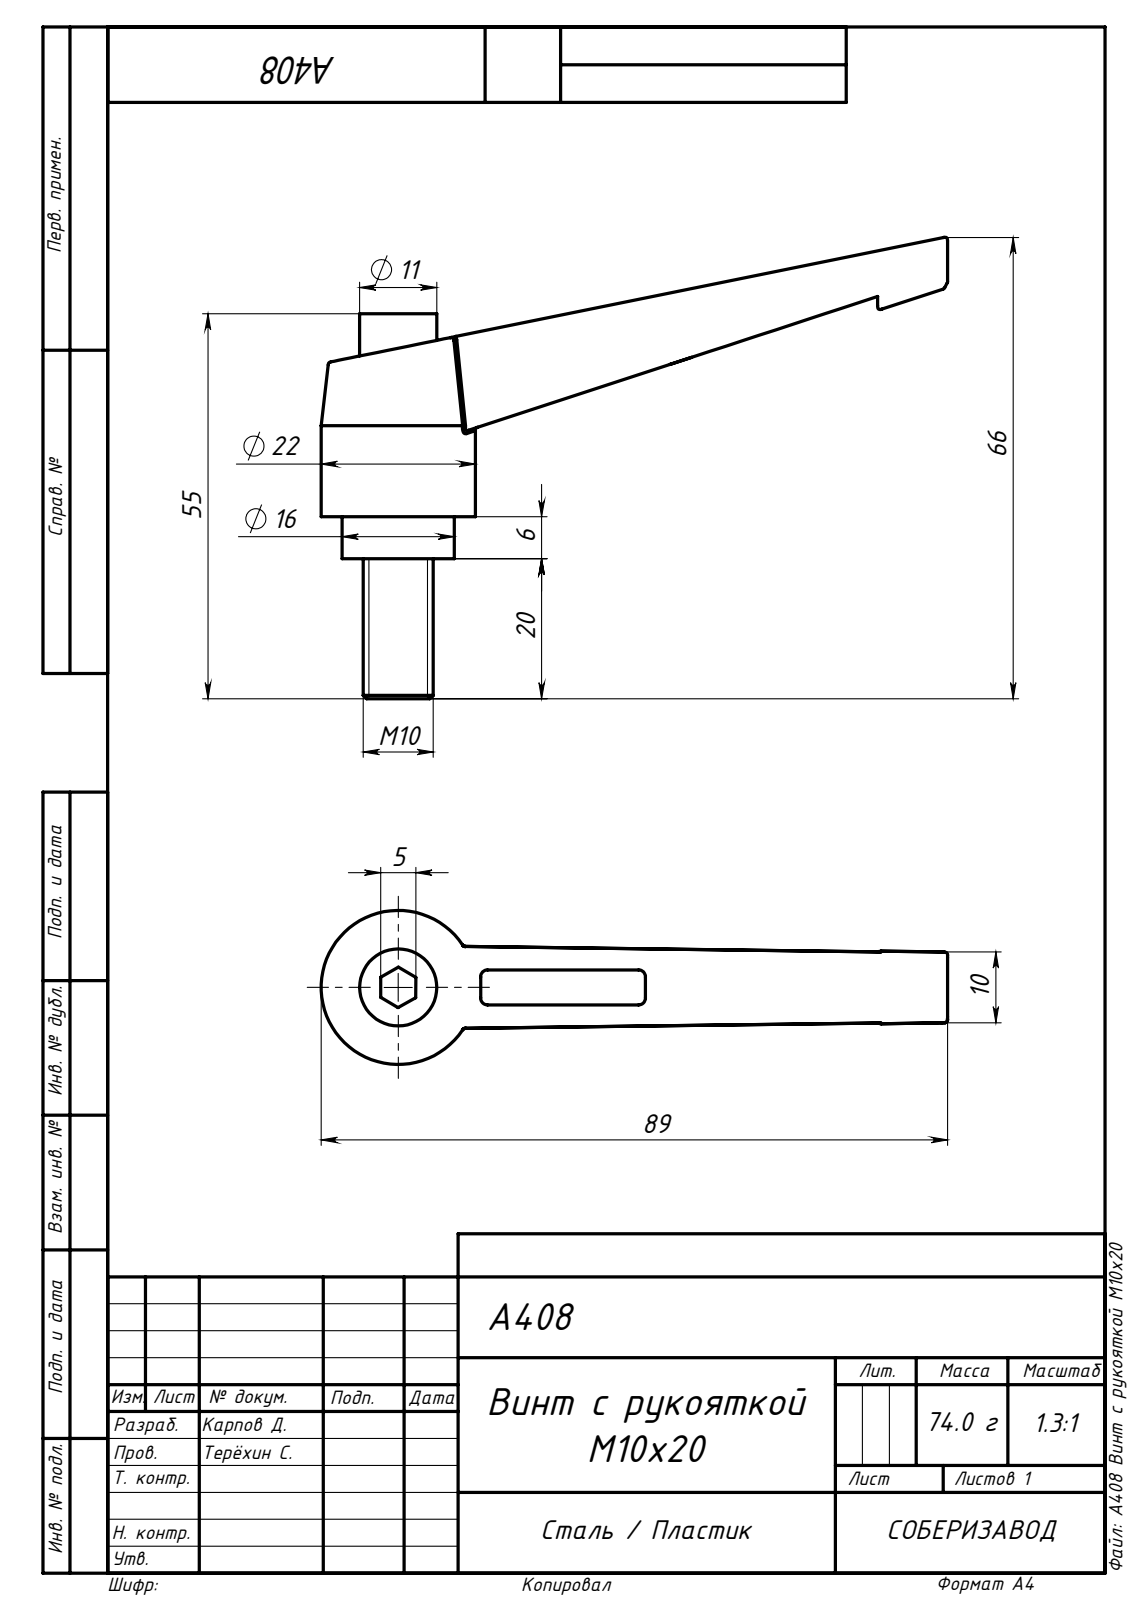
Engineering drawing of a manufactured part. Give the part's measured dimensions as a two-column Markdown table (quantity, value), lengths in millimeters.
| quantity | value |
| --- | --- |
| part name | A408 Винт с рукояткой М10х20 |
| STEP written by | SolidWorks 2020 (AUTOMOTIVE_DESIGN) |
| units | millimeters |
| bodies | 1 solid, 81 faces (31 planar, 12 cylindrical, 38 other) |
| overall size | 89.4 × 65.91 × 22 |
| volume | 15 830 mm³ |
| surface area | 6 893 mm² |
| round bosses / shafts (diameter × count) | 22 × 1, 16 × 1, 11 × 1, 10 × 1 |
| partial cylindrical surfaces (radius × count) | 1 × 4 |
| main face-to-face distances | 6, 0.31, 26, 6.93, 35, 29, 20, 55, 60.59, 5 |
